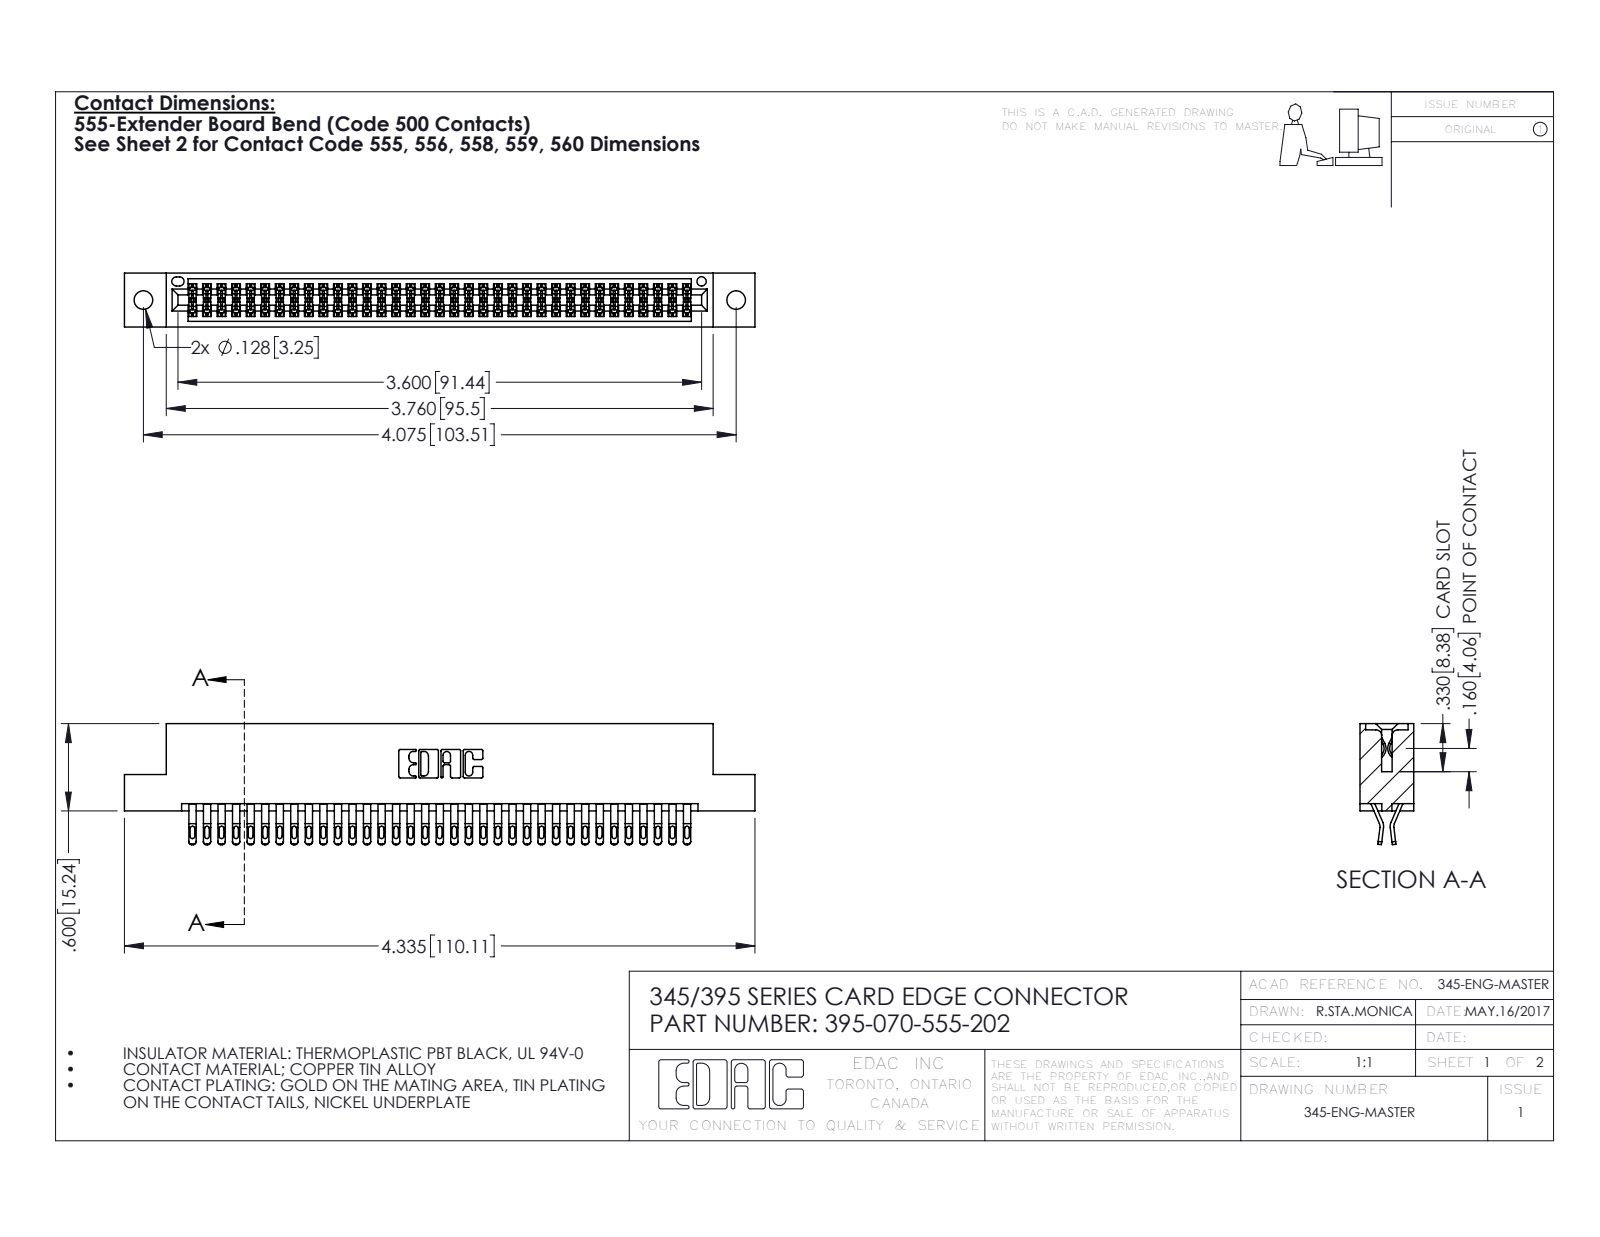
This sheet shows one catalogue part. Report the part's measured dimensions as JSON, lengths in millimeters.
{"part_name": "345 Part_Flush Mounting Lugs - 0.128 Dia; 345-292-001_555 Tail; 395-070-555-202", "step_written_by": "SolidWorks 2016 (CONFIG_CONTROL_DESIGN)", "units": "millimeters", "bodies": {"solids": 71, "faces": 4046, "planar": 2250, "cylindrical": 1796, "other": 0}, "overall_size": [110.1, 21.1, 9.4], "volume_mm3": 10800, "surface_area_mm2": 16260, "round_holes": [[3.3, 2], [1.6, 1]], "partial_cylinders_radius": [[0.4, 175], [0.5, 140], [0.2, 105], [0.3, 22], [0.2, 6], [0.8, 6], [0.7, 3], [0.3, 2]], "face_to_face_distances": [7.6, 1.8, 9.4, 0.6, 5.1, 2.5, 6.9, 5.7, 4.4, 3.8], "hole_center_spacings": [6.9, 97.5, 103.5]}
